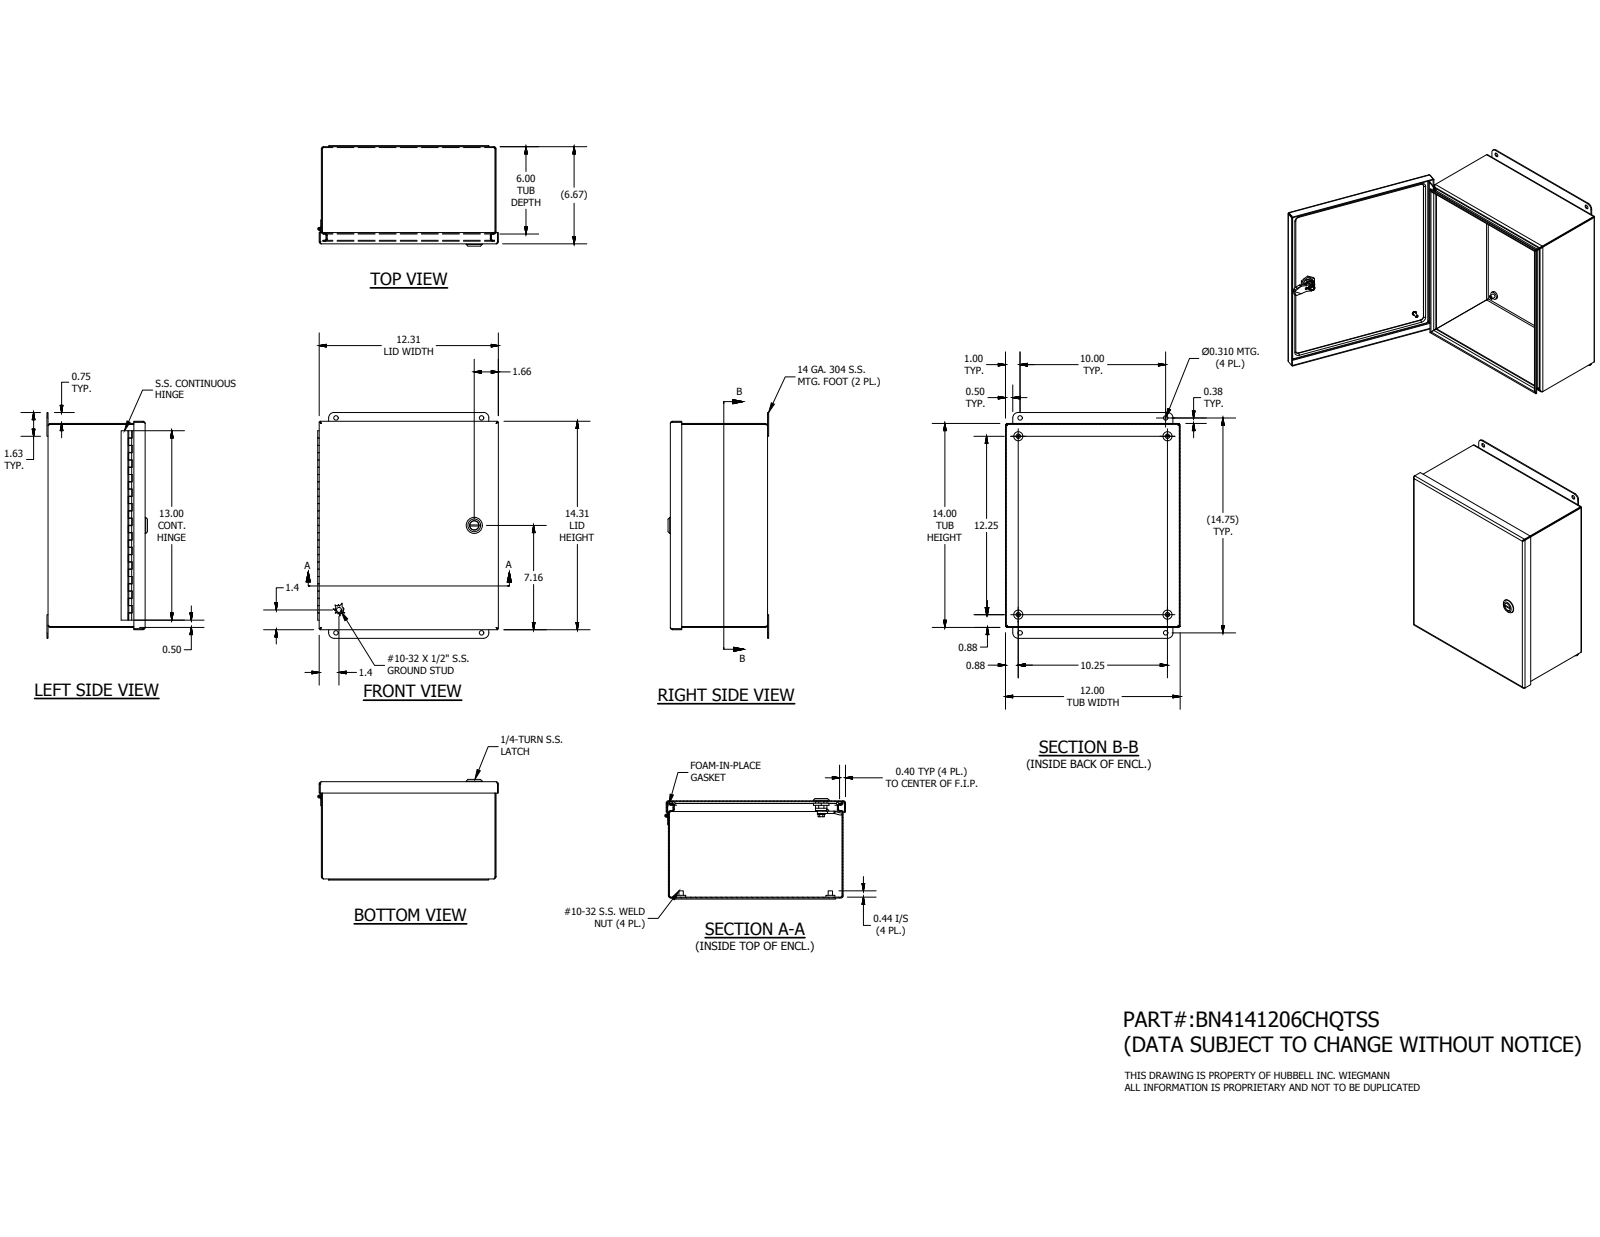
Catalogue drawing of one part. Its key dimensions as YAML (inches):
part_name: "BN41412CHQTSSLID; 14x12; 34856; H4050553LH (+8 more)"
step_written_by: "Autodesk Inventor 2016 (AUTOMOTIVE_DESIGN)"
units: inches
bodies: {solids: 19, faces: 648, planar: 347, cylindrical: 207, other: 94}
overall_size: [15.5, 12.412, 6.905]
volume: 51.96
surface_area: 1662
round_holes:
  - {diameter: 0.156, count: 4}
  - {diameter: 0.31, count: 4}
  - {diameter: 0.117, count: 1}
  - {diameter: 0.197, count: 1}
  - {diameter: 0.315, count: 1}
  - {diameter: 0.394, count: 1}
  - {diameter: 0.402, count: 1}
  - {diameter: 0.634, count: 1}
round_bosses_or_shafts:
  - {diameter: 0.625, count: 4}
  - {diameter: 0.3, count: 4}
  - {diameter: 1.102, count: 1}
  - {diameter: 0.78, count: 1}
  - {diameter: 0.63, count: 1}
  - {diameter: 0.598, count: 1}
  - {diameter: 0.531, count: 1}
  - {diameter: 0.504, count: 1}
partial_cylinders:
  - {radius: 0.094, count: 20}
  - {radius: 0.153, count: 20}
  - {radius: 0.125, count: 16}
  - {radius: 0.02, count: 8}
  - {radius: 0.157, count: 4}
  - {radius: 0.375, count: 4}
  - {radius: 0.091, count: 2}
  - {radius: 0.254, count: 1}
face_to_face_distances: [0.059, 0.059, 6.614, 6.672, 6.555, 6.613, 13.941, 11.941, 12, 11.941]
hole_center_spacings: [1.256, 13.5, 10, 10.202, 10.202, 10.25, 12.026, 12.25]
